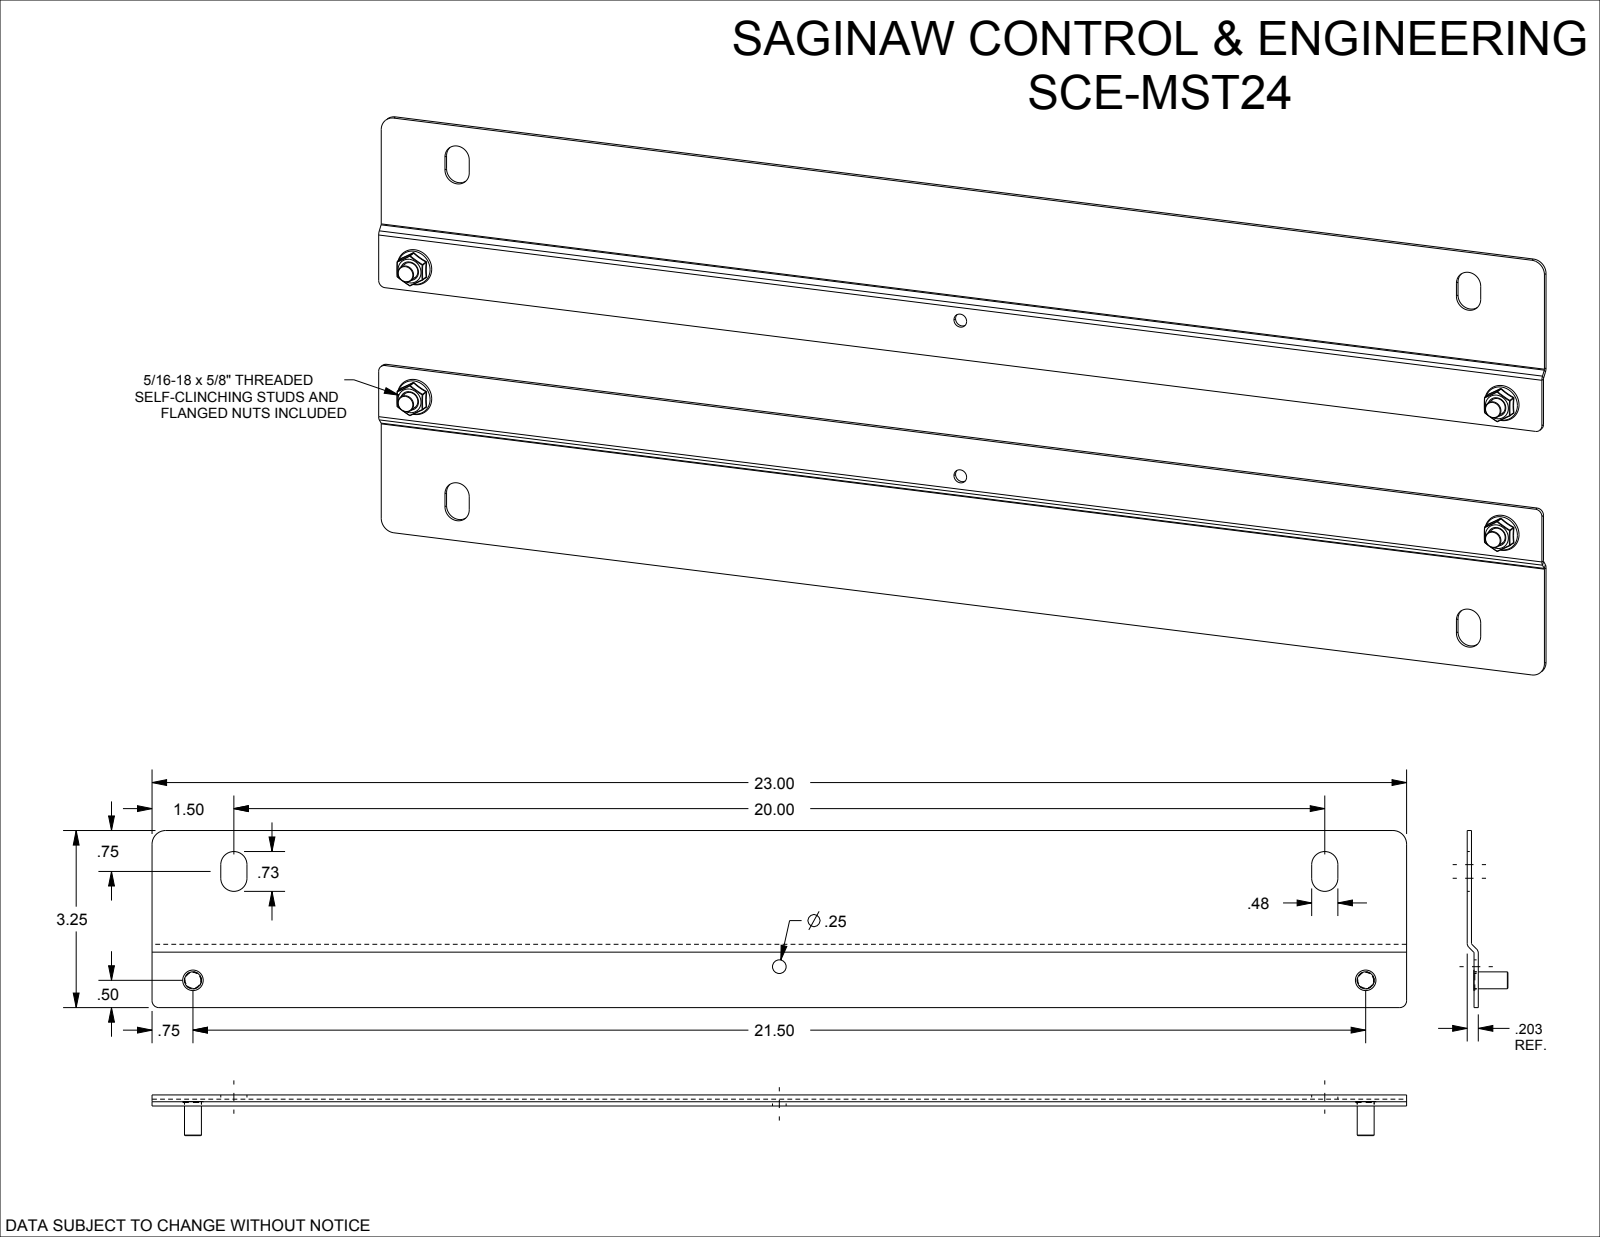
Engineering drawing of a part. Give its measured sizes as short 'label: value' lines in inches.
name: SCE-MST24
written by: SolidWorks 2019 (AUTOMOTIVE_DESIGN)
unit: in
bodies: 10 solids, 258 faces (72 planar, 66 cylindrical, 120 other)
size: 23 × 7.99 × 0.746
volume: 12.07 in³; area: 316.9 in²
holes: 4× ⌀0.312, 2× ⌀0.25
bosses: 4× ⌀0.376, 4× ⌀0.31
rounds: 24× R0.01, 8× R0.24, 4× R0.023, 4× R0.101, 4× R0.125, 4× R0.25
face distances: 0.078, 0.078, 0.047, 0.125, 0.125, 0.203, 3.245, 4.745, 1.5, 7.99
hole spacings: 10.753, 11.096, 2.5, 21.5, 21.645, 3
